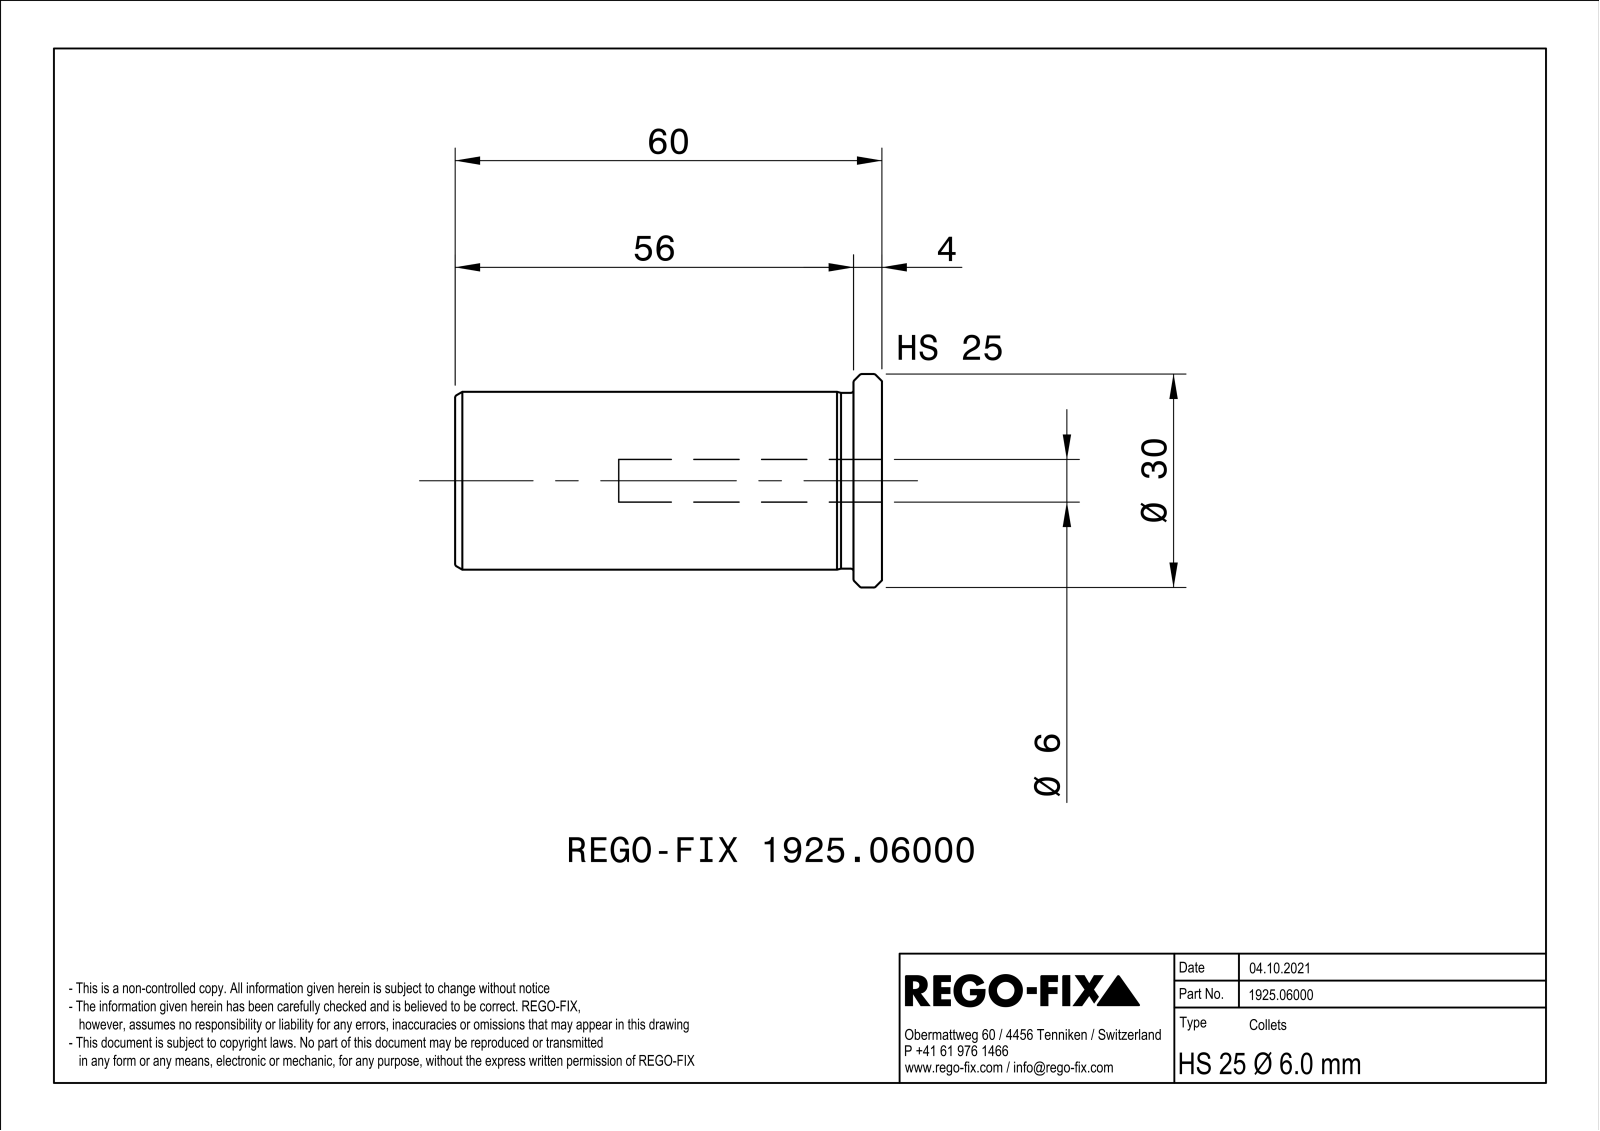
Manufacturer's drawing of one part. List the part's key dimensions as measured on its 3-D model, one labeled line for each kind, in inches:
Part name (STEP PRODUCT): NOCUT
STEP written by: SIEMENS PLM Software Solid Edge ST10 (AUTOMOTIVE_DESIGN)
Units: inches
Bodies: 1 solid, 73 faces (22 planar, 12 cylindrical, 39 other)
Overall size (bounding box): 2.362 × 1.181 × 1.181
Volume: 1.425 in³ · Surface area: 15.23 in²
Round holes (diameter × count): ⌀0.236 ×1, ⌀0.394 ×1, ⌀0.807 ×1
Round bosses / shafts (diameter × count): ⌀1.181 ×1, ⌀0.984 ×1, ⌀0.972 ×1
Main face-to-face distances: 0.031, 0.157, 2.362, 2.205
